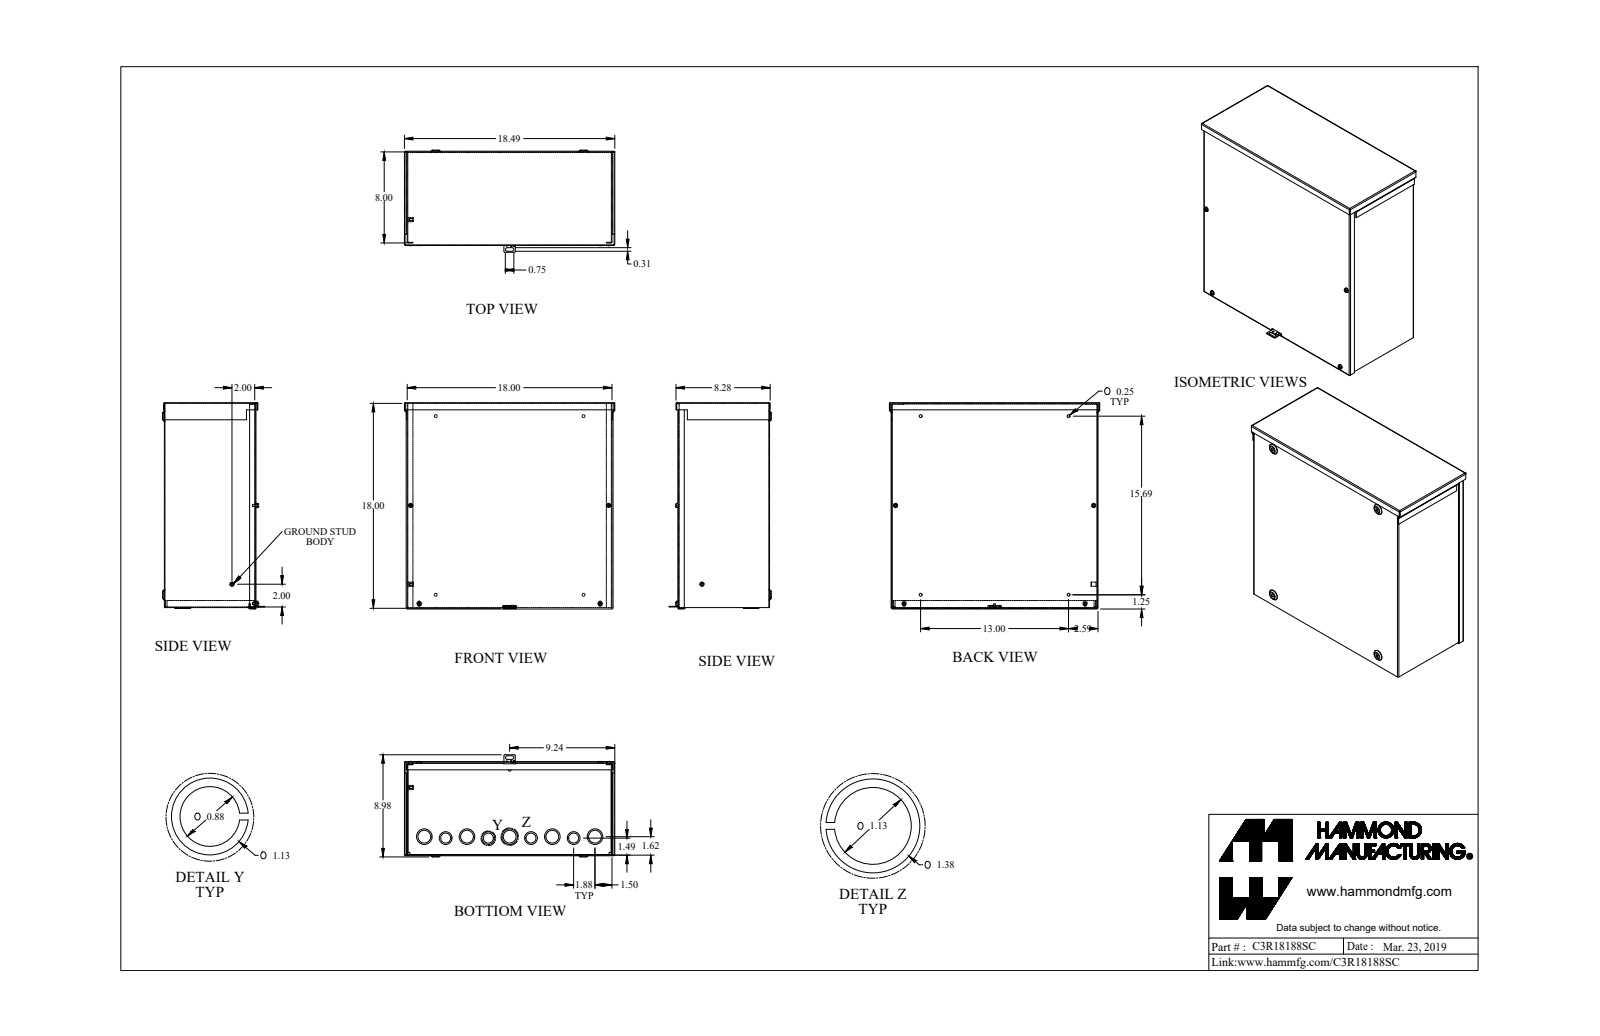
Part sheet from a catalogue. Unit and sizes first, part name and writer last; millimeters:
Units: millimetres
Overall size (bounding box): 469.6 × 460.2 × 228
Round holes (diameter × count): ⌀4.3 ×4, ⌀6.4 ×4, ⌀28.6 ×3, ⌀22.2 ×2, ⌀22.2 ×2, ⌀28.6 ×2, ⌀3.2 ×1, ⌀3.5 ×1, ⌀4 ×1
Round bosses / shafts (diameter × count): ⌀28.6 ×4, ⌀4.8 ×4, ⌀34.9 ×3, ⌀9.5 ×3, ⌀34.9 ×2, ⌀9.5 ×2, ⌀3.2 ×1
Partial cylindrical surfaces — rounded edges, fillets, slot ends (radius × count): R0.7 ×21, R2.2 ×21, R2.8 ×8, R3.2 ×8, R4 ×2
Main face-to-face distances: 1.4, 203.2, 455.8, 201.8, 204.6, 457.2, 1.4, 454.3, 454.3, 455.8
Hole centre spacings: 95.3, 47.7, 47.8, 142.9, 190.5, 207, 434.6, 238.2
Volume: 1 265 000 mm³ · Surface area: 1 755 000 mm²
Bodies: 11 solids, 457 faces (238 planar, 133 cylindrical, 86 other)
Part name (STEP PRODUCT): C3R18188SC_Default
STEP written by: SolidWorks 2019 (CONFIG_CONTROL_DESIGN)
